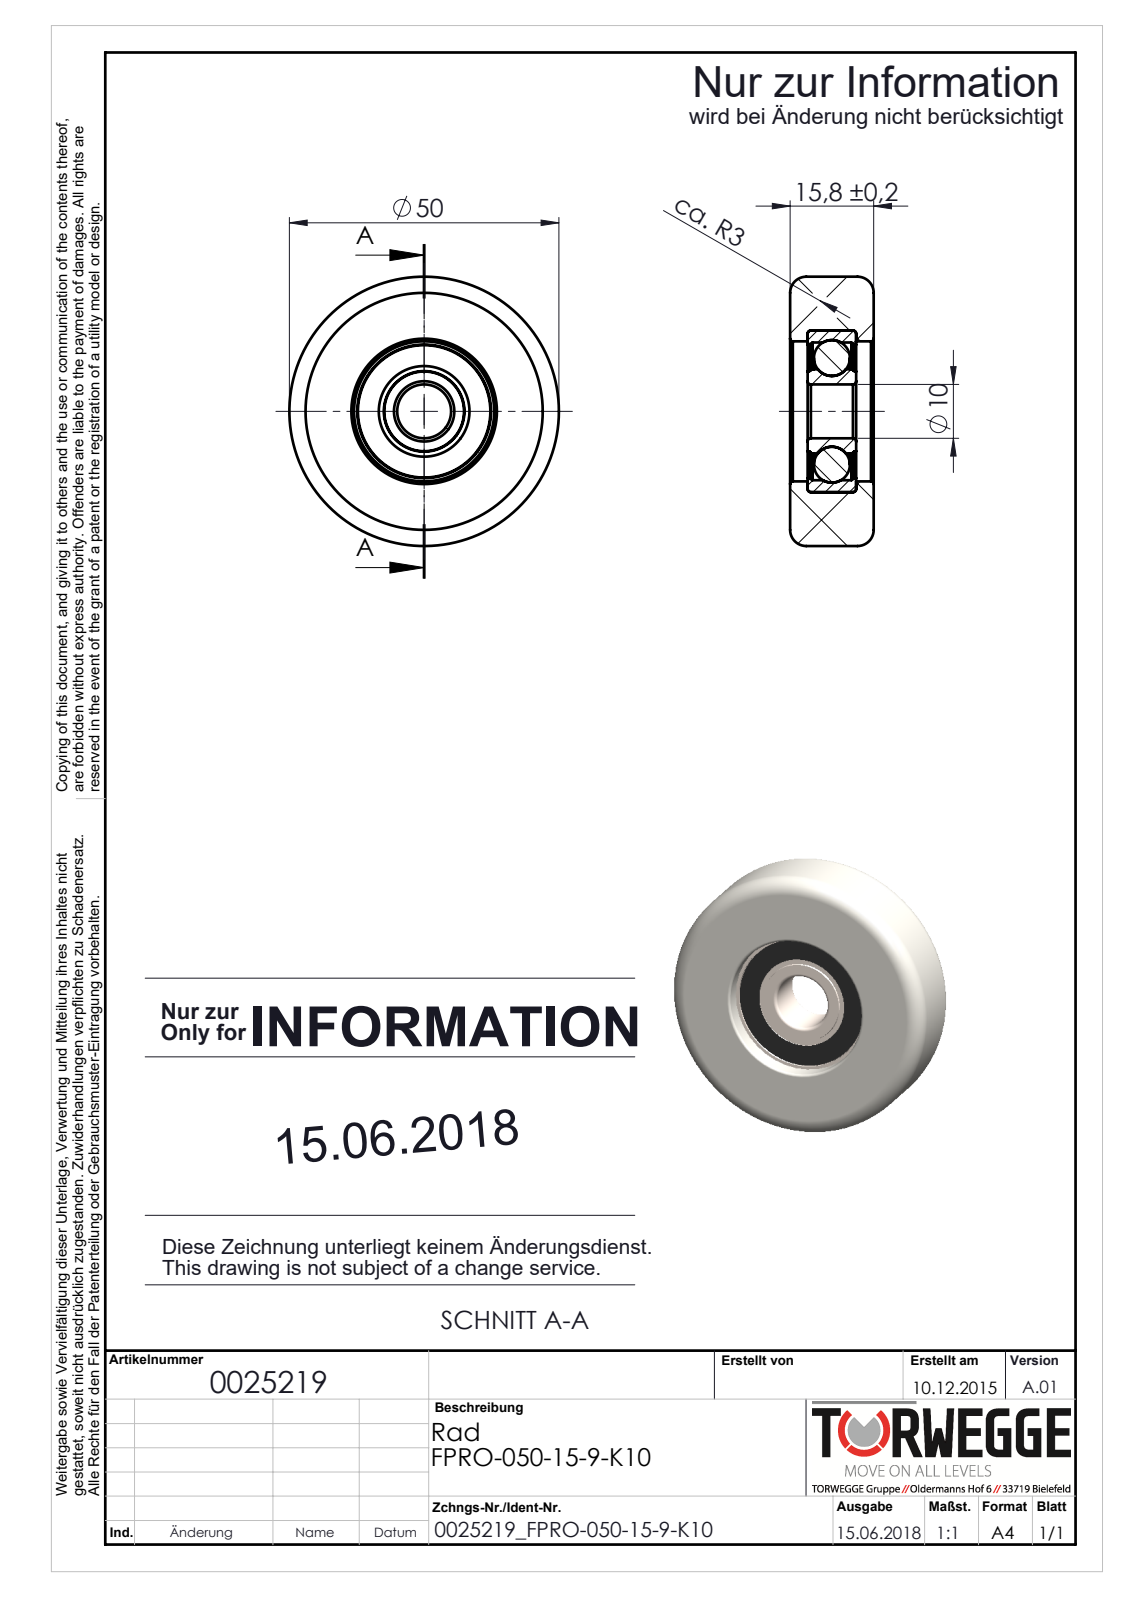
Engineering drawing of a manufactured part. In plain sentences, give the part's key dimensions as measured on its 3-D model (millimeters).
The part is named "0025219_FPRO-050-15-9-K10; Rillenkugellager_DIN625-6200-2RS; 0025219_FPRO-050-15-9-K10-Bandage". Its 3-D file was written by "SolidWorks 2018 (AUTOMOTIVE_DESIGN)". It is 6 solids with 104 faces: 18 planar, 40 cylindrical and 46 other. Overall it measures 50 by 50 by 15.5 millimeters. Its volume is 24 857 cubic millimeters and its surface area 12 158 square millimeters. Round holes: 1 of diameter 10, 1 of diameter 16.83, 1 of diameter 22.89, 1 of diameter 24.8, 1 of diameter 25.56, 1 of diameter 26, 1 of diameter 30. Round bosses or shafts: 1 of diameter 50, 1 of diameter 24.58, 1 of diameter 15.62. The main face-to-face distances are 15.5, 3.25, 12.25, 3.42, 12.08, 8.83, 8.38, 3.7, 11.8, 0.45.
